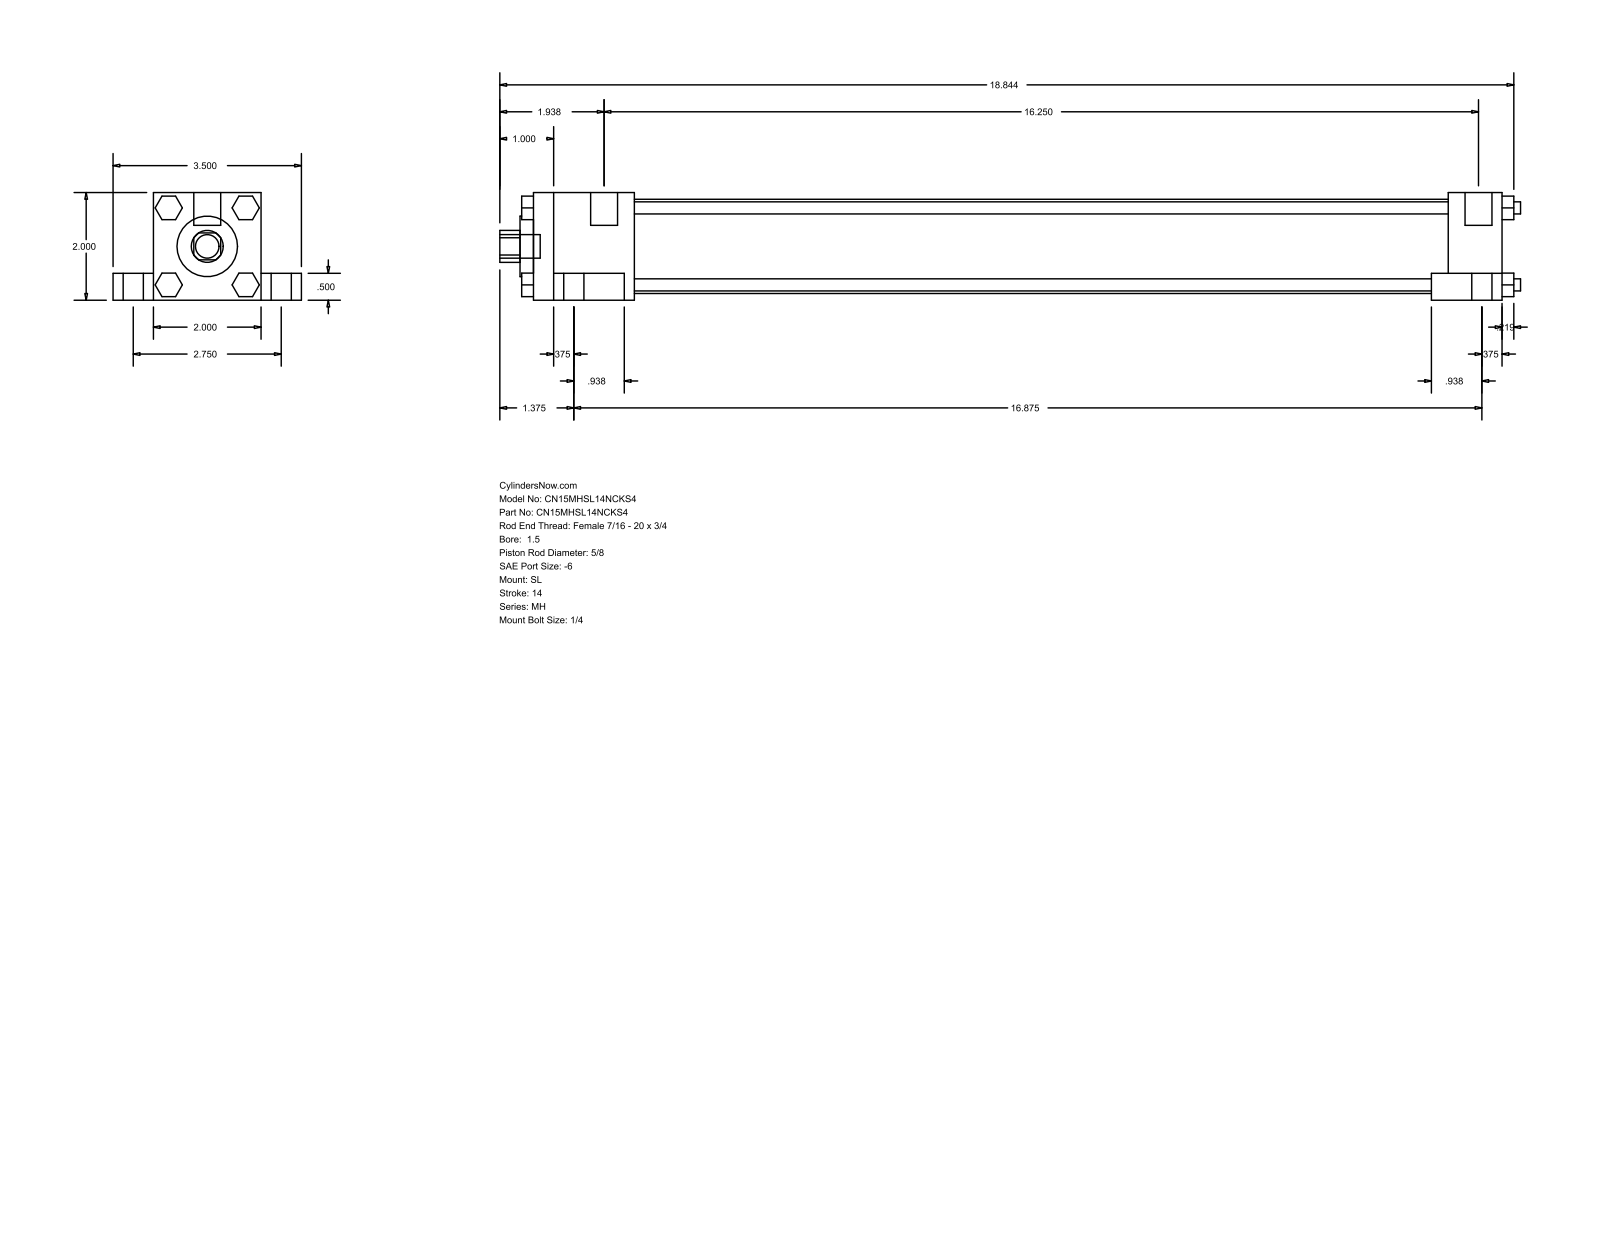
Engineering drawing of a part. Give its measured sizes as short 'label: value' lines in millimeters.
name: MH_SL__0150_0.625
written by: GSSL Pune (CONFIG_CONTROL_DESIGN)
unit: mm
bodies: 0 solids, 148 faces (112 planar, 36 cylindrical, 0 other)
size: 481.81 × 88.9 × 50.8
holes: 1× ⌀15.88, 1× ⌀28.57, 1× ⌀44.45
bosses: 4× ⌀15.88, 4× ⌀9.53, 4× ⌀5.71, 4× ⌀5.56, 2× ⌀12.7, 1× ⌀11.11
rounds: 1× R7.54
face distances: 50.8, 38.1, 19.05, 12.7, 69.85, 457.19, 9.52, 431.8, 25.39, 47.62
